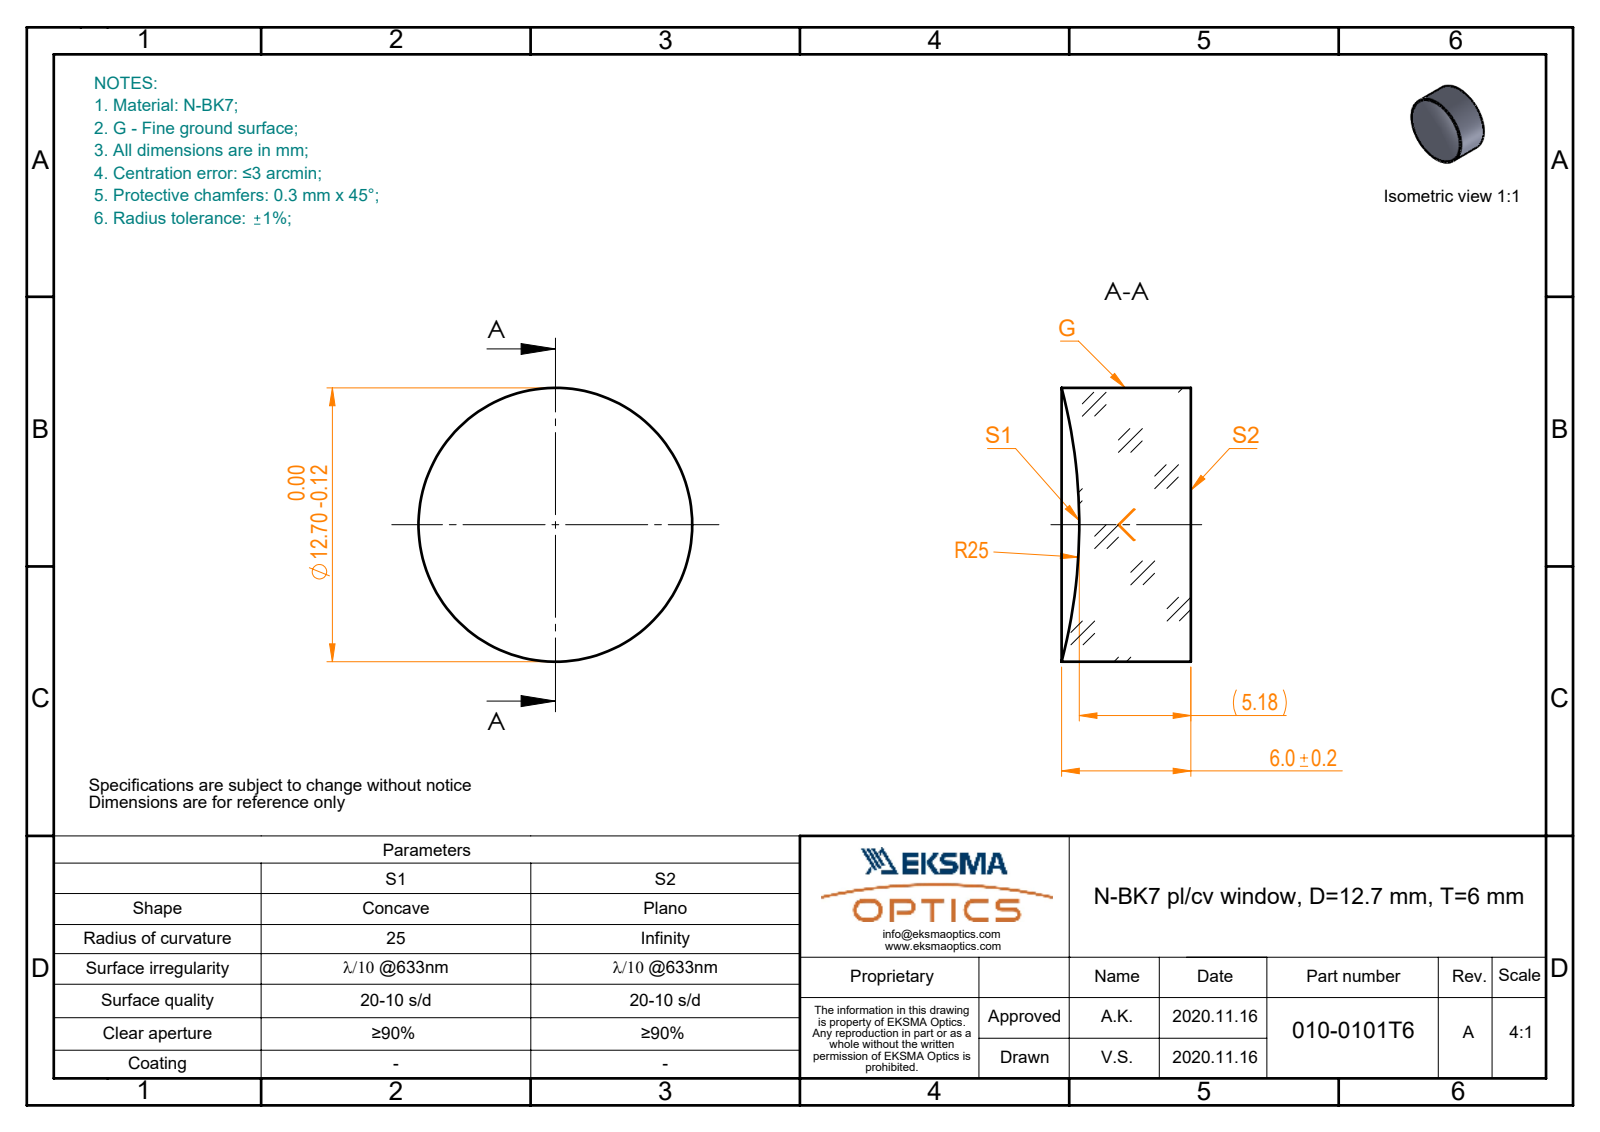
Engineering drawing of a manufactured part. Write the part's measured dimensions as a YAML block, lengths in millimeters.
part_name: "010-0101T6_N-BK7_PCV_window"
step_written_by: "SolidWorks 2019 (CONFIG_CONTROL_DESIGN)"
units: millimeters
bodies: {solids: 1, faces: 5, planar: 1, cylindrical: 2, other: 2}
overall_size: [12.7, 12.7, 6]
volume: 708
surface_area: 495
round_bosses_or_shafts:
  - {diameter: 12.7, count: 1}
